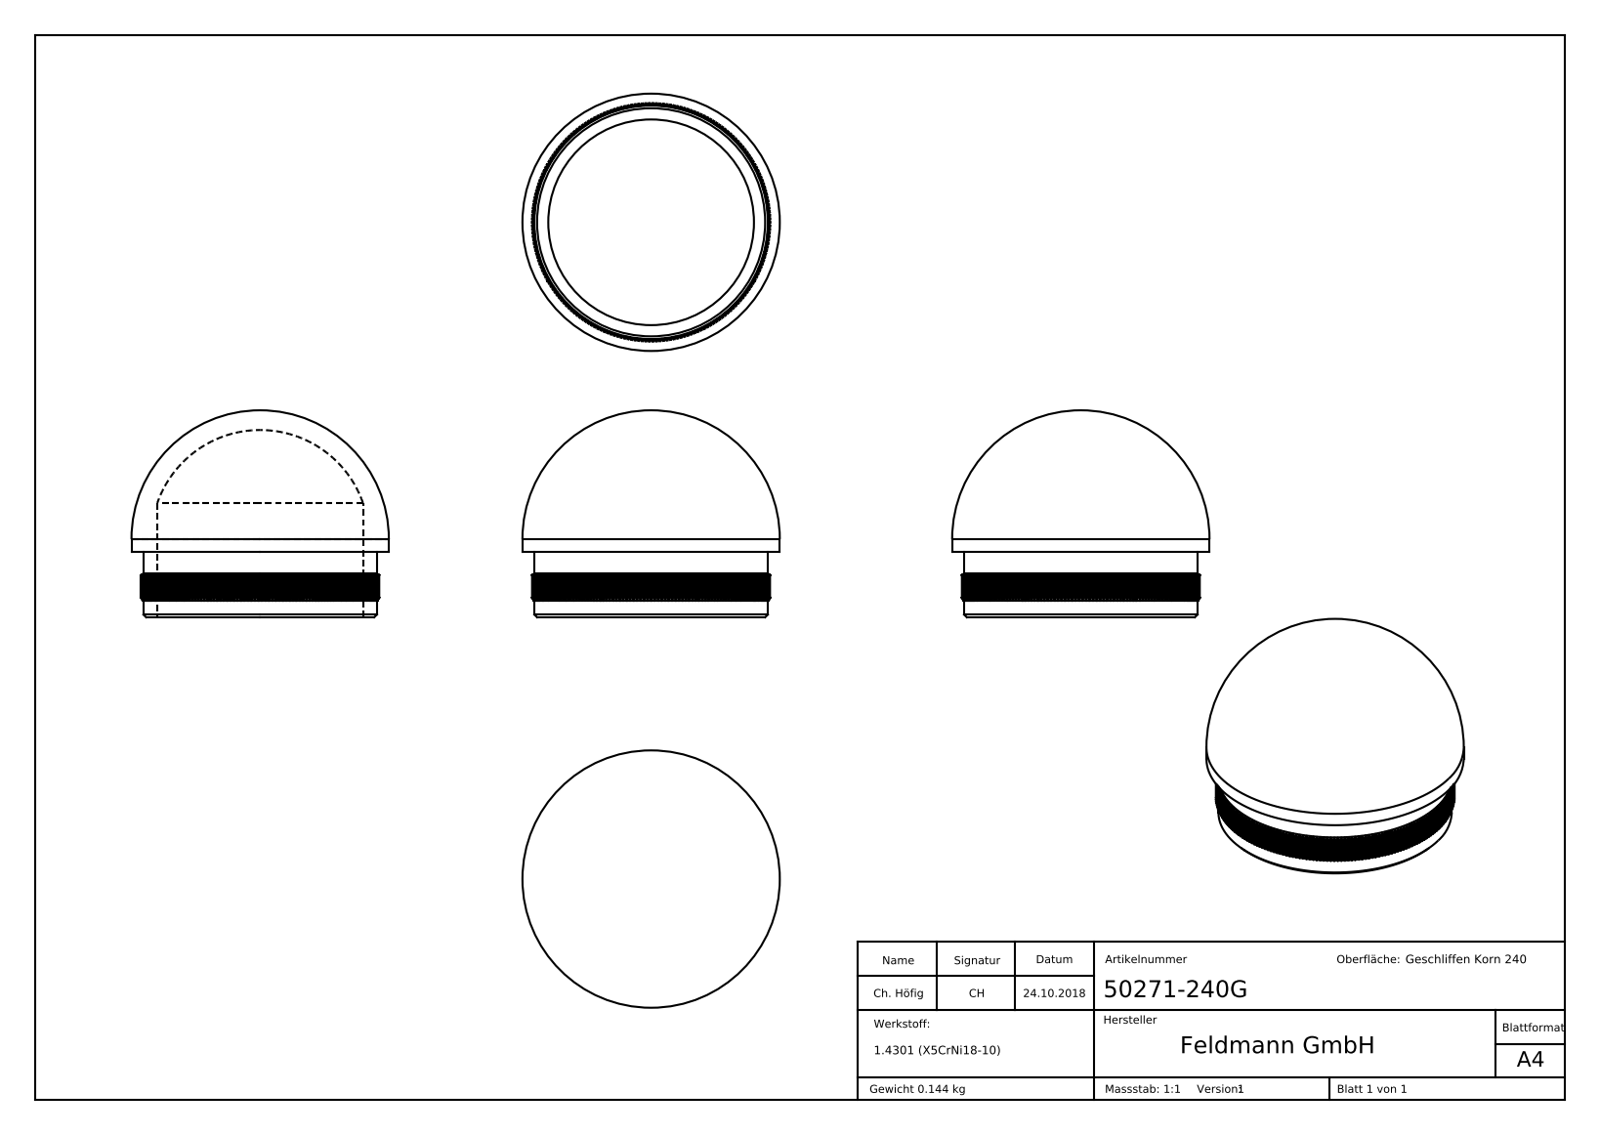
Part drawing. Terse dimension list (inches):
name: 50271-240G
written by: SolidWorks 2015 (CONFIG_CONTROL_DESIGN)
unit: in
bodies: 1 solid, 1087 faces (528 planar, 245 cylindrical, 314 other)
size: 1.902 × 1.902 × 1.53
volume: 1.111 in³; area: 17.32 in²
holes: 1× ⌀1.52
bosses: 1× ⌀1.902, 1× ⌀1.724
rounds: 1× R0.764, 1× R0.88
face distances: 0.866, 0.48, 0.866, 0.867, 0.865, 0.867, 0.126, 0.354, 0.042, 0.037
